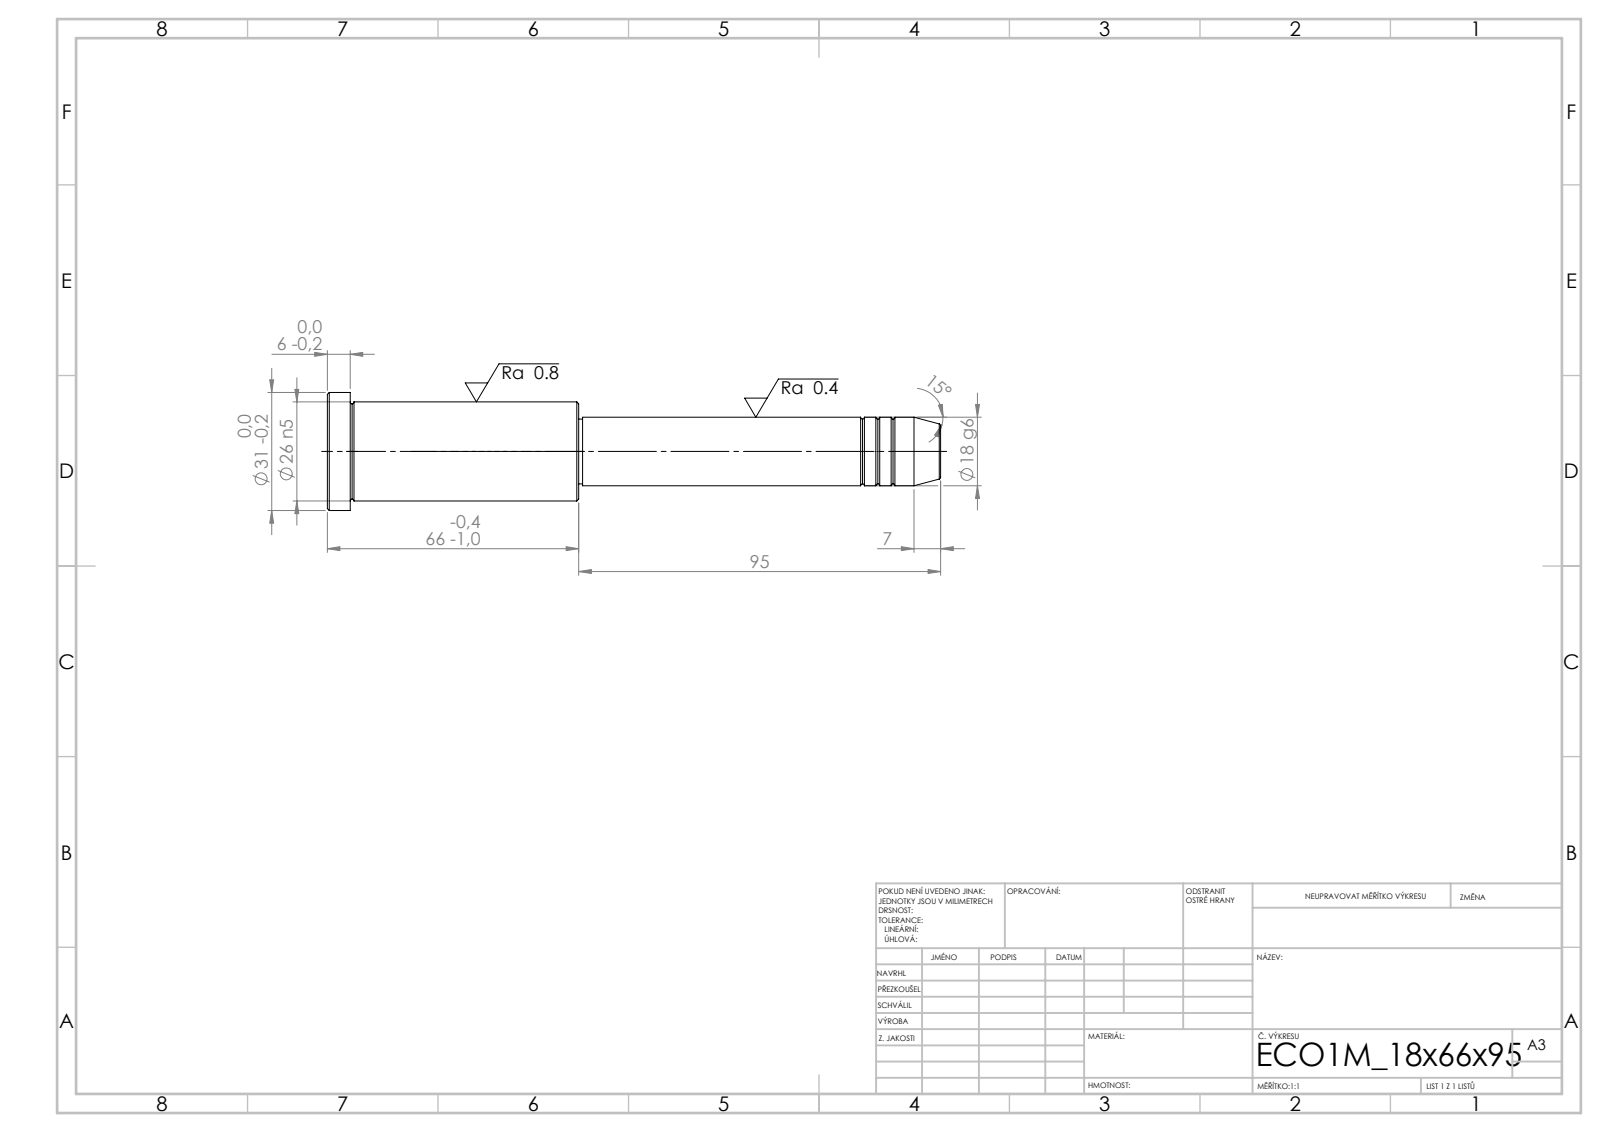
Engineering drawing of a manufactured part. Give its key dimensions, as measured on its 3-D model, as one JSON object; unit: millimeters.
{"step_written_by": "SolidWorks 2019 (CONFIG_CONTROL_DESIGN)", "units": "millimeters", "bodies": {"solids": 1, "faces": 43, "planar": 5, "cylindrical": 14, "other": 24}, "overall_size": [161, 31, 31], "volume_mm3": 60066, "surface_area_mm2": 12368, "round_bosses_or_shafts": [[31, 1], [26, 1], [18, 1], [17, 1]], "face_to_face_distances": [66, 60, 6, 95, 155, 161, 94, 1, 61, 67]}
